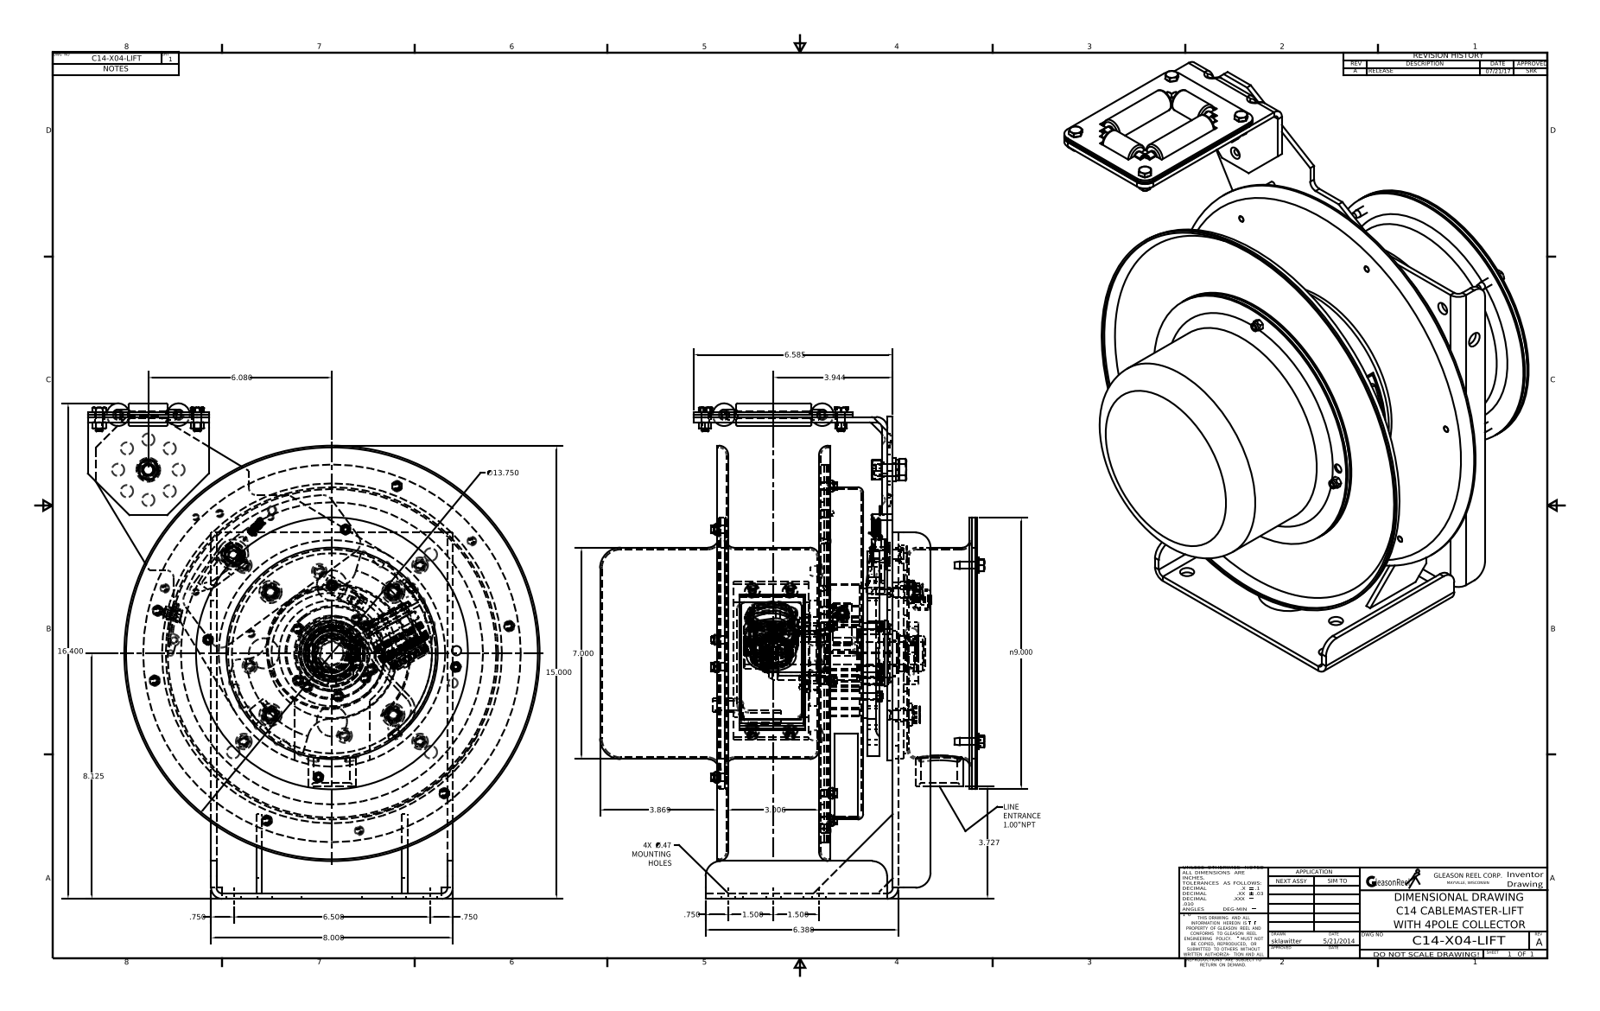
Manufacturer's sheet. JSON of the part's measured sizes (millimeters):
{"part_name": "C14-X04-LIFT (SW)", "step_written_by": "Autodesk Inventor 2016 (AUTOMOTIVE_DESIGN)", "units": "millimeters", "bodies": {"solids": 157, "faces": 3177, "planar": 1254, "cylindrical": 1028, "other": 895}, "overall_size": [416.56, 379.86, 323.2], "volume_mm3": 2657000, "surface_area_mm2": 2232000, "round_holes": [[6.35, 26], [5, 24], [4.13, 19], [10.31, 13], [5.56, 12], [5.41, 8], [10.67, 8], [11.94, 6], [25.4, 6], [7.14, 5], [7.98, 5], [4.57, 4]], "round_bosses_or_shafts": [[5, 24], [6.8, 10], [10, 7], [6, 6], [12.7, 5], [11.6, 5], [8, 5], [19.05, 4]], "partial_cylinders_radius": [[0.76, 67], [0.24, 64], [0.38, 58], [1.98, 18], [0.16, 16], [1.52, 12], [6.35, 8], [9.53, 8]], "face_to_face_distances": [1.52, 3.17, 6.19, 30.93, 126.76, 4.69, 1.5, 4.67, 4.54, 84.04], "hole_center_spacings": [150.71, 19.44, 25.4, 31.75, 35.92, 46.93, 51.91, 51.93]}
